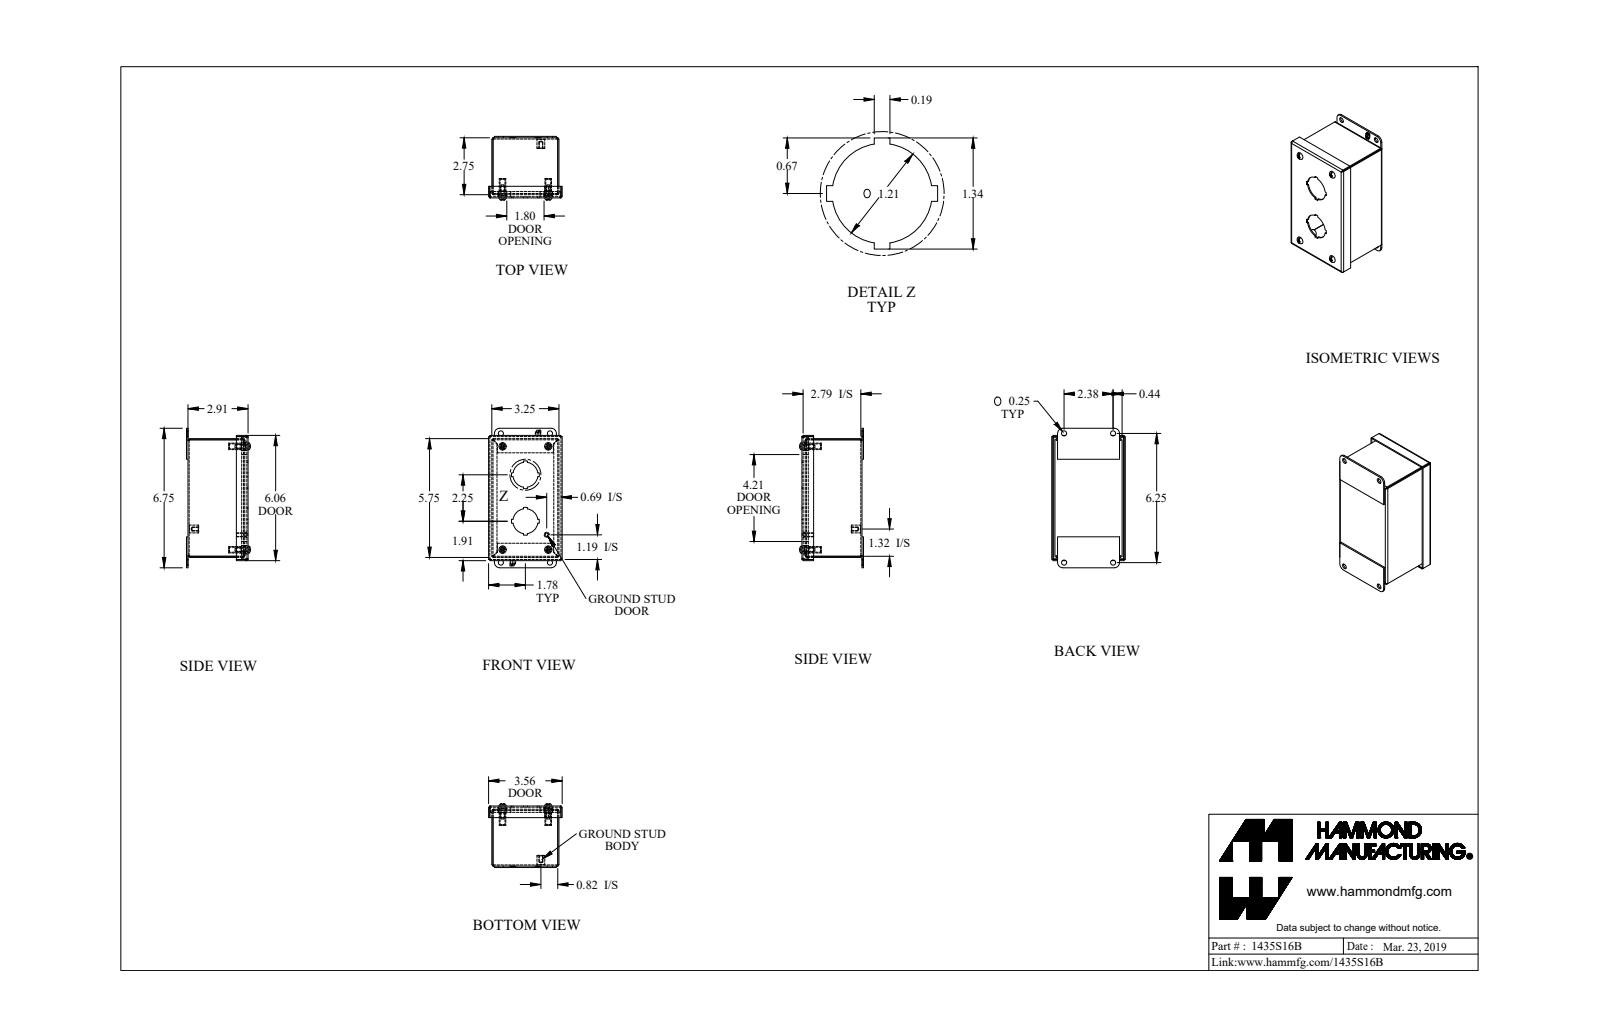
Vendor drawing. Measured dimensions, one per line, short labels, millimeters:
name: 1435S16B_Default
written by: SolidWorks 2019 (CONFIG_CONTROL_DESIGN)
unit: mm
bodies: 19 solids, 477 faces (307 planar, 140 cylindrical, 30 other)
size: 171.5 × 90.5 × 78.5
volume: 135 200 mm³; area: 164 600 mm²
holes: 8× ⌀6.4, 4× ⌀1.7, 4× ⌀6.1, 4× ⌀6.4, 4× ⌀10.3, 2× ⌀30.7, 1× ⌀4
bosses: 5× ⌀4.8, 4× ⌀10.3, 4× ⌀8, 4× ⌀3.8, 1× ⌀9.5, 1× ⌀6.4
rounds: 12× R0.7, 12× R2.2, 4× R4.3, 4× R6.4
face distances: 1.4, 72.4, 1.4, 81.1, 73.8, 70.9, 144.6, 79.7, 82.6, 4
hole spacings: 127, 16, 16, 56.2, 60.4, 60.4, 138.9, 142.9
